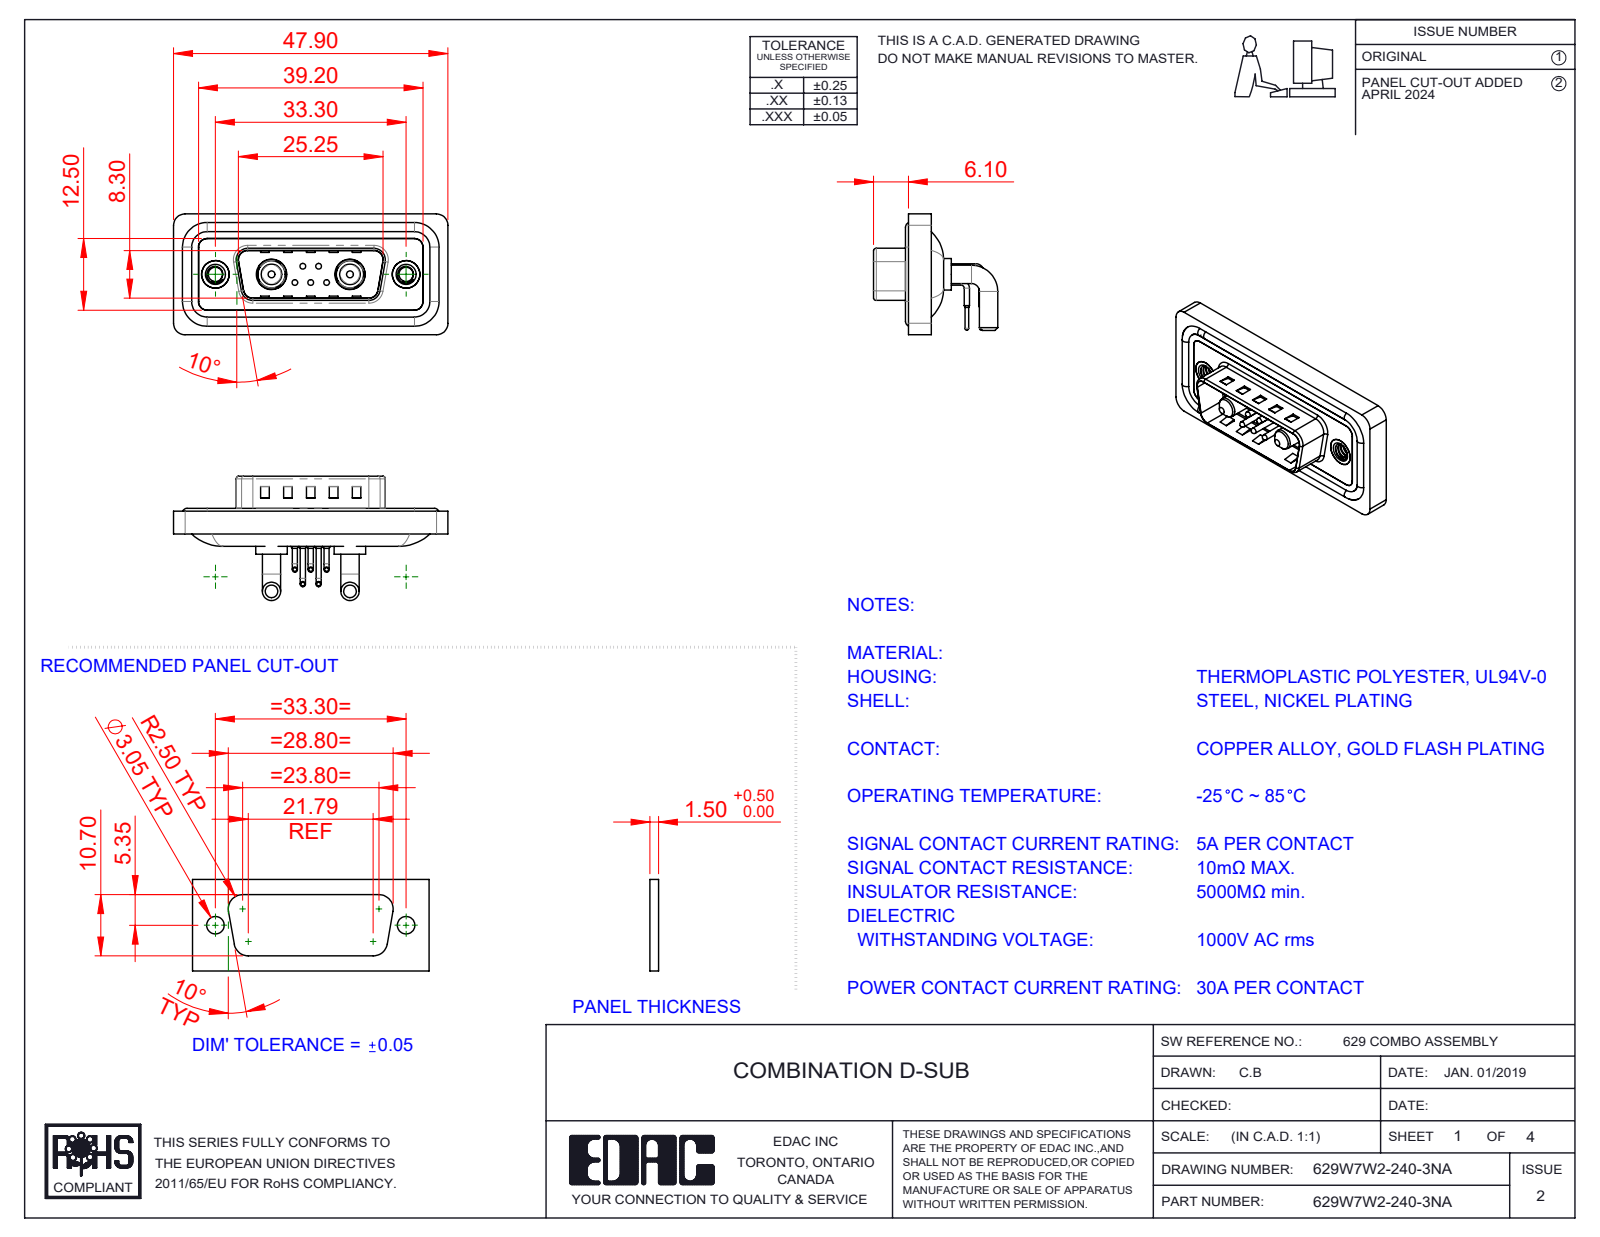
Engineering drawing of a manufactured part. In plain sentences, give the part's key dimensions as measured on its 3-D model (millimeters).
The part is named "629Combo Waterproof Housing_15 Contacts; 629Combo Shell Rear_15 Contacts; Power Pin_30A RA; 629Combo Contact Row 1 (+5 more)". Its 3-D file was written by "SolidWorks 2023 (CONFIG_CONTROL_DESIGN)". It is 16 solids with 1077 faces: 517 planar, 404 cylindrical and 156 other. Overall it measures 47.9 by 21.7 by 21.1 millimeters. Its volume is 5 740 cubic millimeters and its surface area 9 181 square millimeters. Round holes: 5 of diameter 0.75, 5 of diameter 1.6, 5 of diameter 2, 2 of diameter 2.5, 2 of diameter 4, 2 of diameter 4.8, 2 of diameter 4.85, 2 of diameter 5, 2 of diameter 5.3. Round bosses or shafts: 10 of diameter 0.9, 5 of diameter 1.5, 5 of diameter 1, 5 of diameter 0.65, 4 of diameter 3.2, 4 of diameter 1.6, 2 of diameter 5.5, 2 of diameter 5.2. Partial cylindrical surfaces (rounded edges, fillets, slot ends): 20 of radius 2, 18 of radius 1.5, 8 of radius 0.5, 8 of radius 1.6, 5 of radius 1.01, 4 of radius 0.25, 4 of radius 0.6, 4 of radius 0.65. The main face-to-face distances are 0.4, 2.9, 0.8, 1.1, 2.1, 1.6, 2.5, 3.1, 4.5, 4.1. The hole center spacings are 3.16, 2.77, 9.8, 23.5, 4.31, 4.33, 5.03, 5.04.
